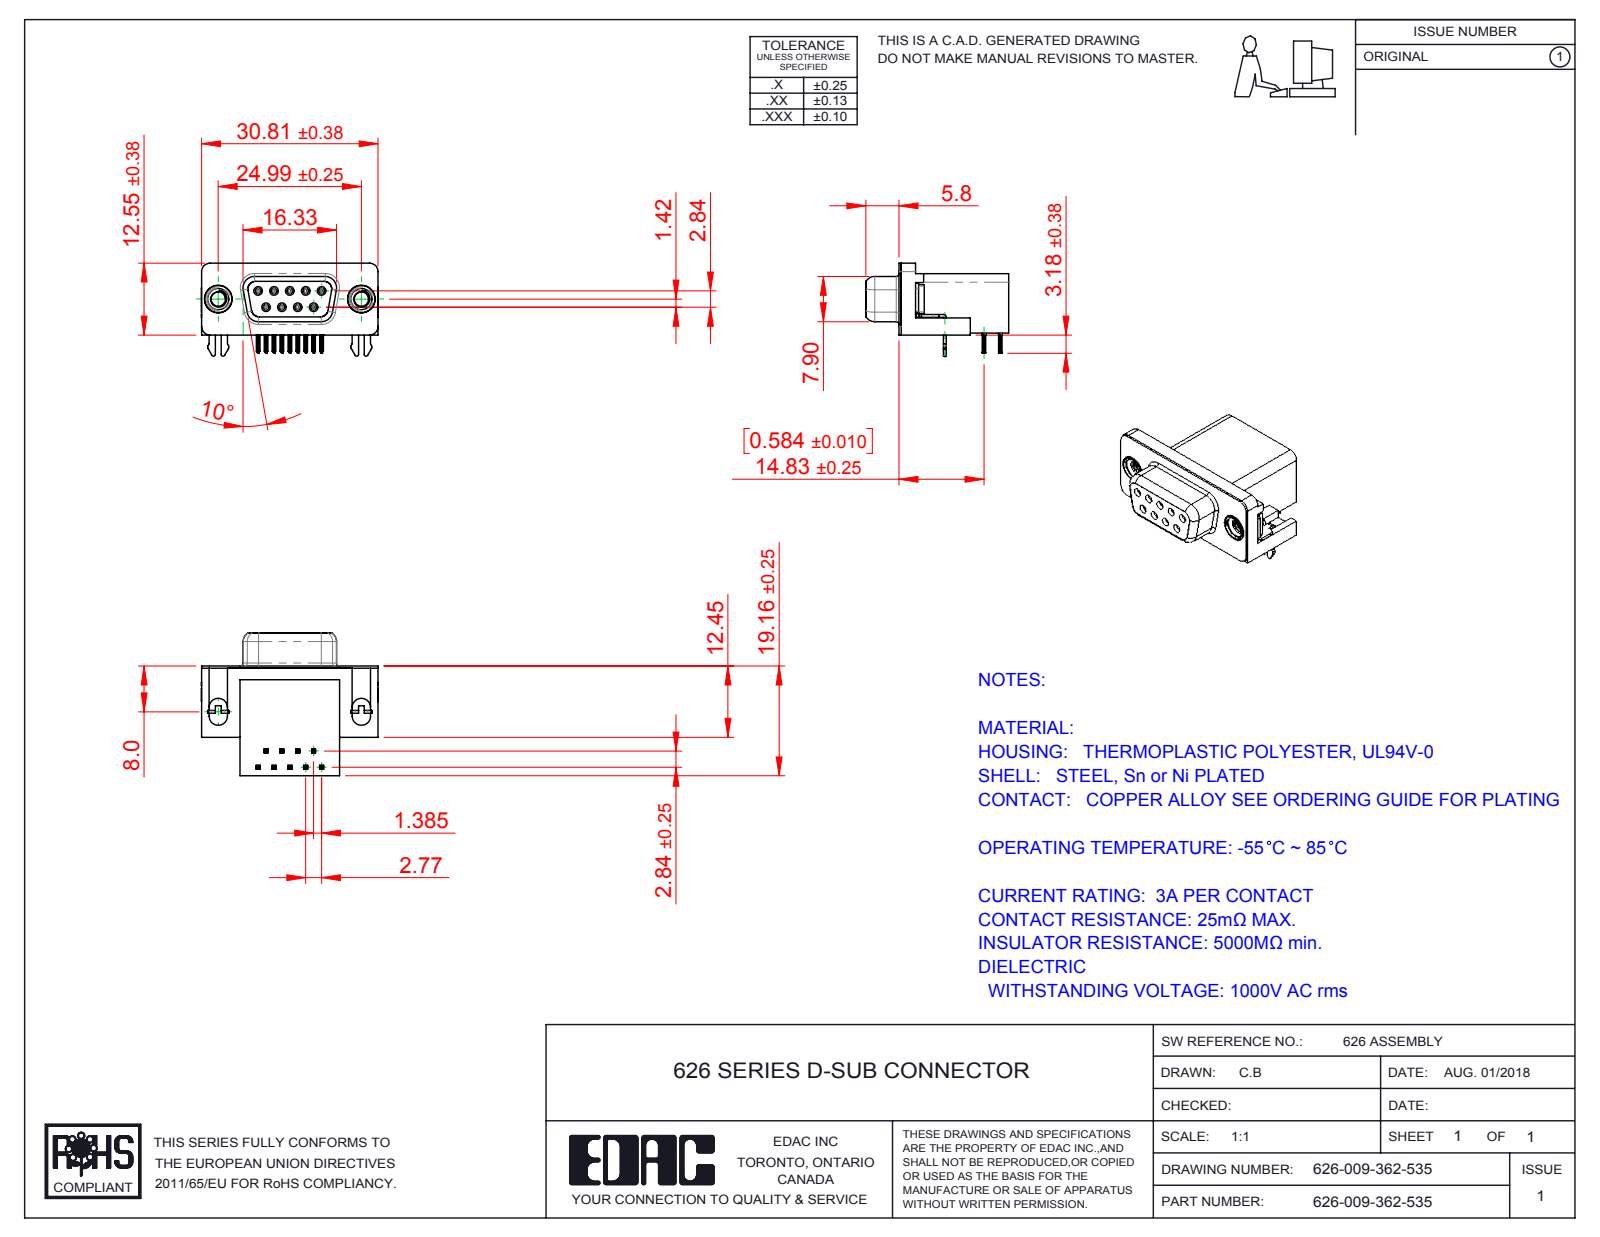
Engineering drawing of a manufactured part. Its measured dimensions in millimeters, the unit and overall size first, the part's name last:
Units: millimetres
Overall size (bounding box): 30.89 × 24.96 × 16.25
Round holes (diameter × count): ⌀0.8 ×9, ⌀0.9 ×9, ⌀2.5 ×2, ⌀4 ×2, ⌀4.8 ×2, ⌀5 ×2
Round bosses / shafts (diameter × count): ⌀1.2 ×9, ⌀4.9 ×2, ⌀4.75 ×2, ⌀3.9 ×2
Partial cylindrical surfaces — rounded edges, fillets, slot ends (radius × count): R0.1 ×72, R0.15 ×36, R0.35 ×18, R1 ×18, R0.5 ×10, R0.34 ×9, R0.25 ×8, R1.35 ×8
Main face-to-face distances: 0.4, 10.34, 0.35, 18.76, 19.16, 2.9, 2.5, 6.2, 16.26, 0.5
Hole centre spacings: 3.16, 2.77, 5.54, 5.03, 5.04, 8.31, 7.48, 7.49
Volume: 4 962 mm³ · Surface area: 5 800 mm²
Bodies: 15 solids, 1612 faces (716 planar, 428 cylindrical, 468 other)
Part name (STEP PRODUCT): 626 Contact Bottom; 626 Contact Top; 626 2 Prong Board Lock; 626 M3 Threaded Rivet (+3 more)
STEP written by: SolidWorks 2016 (CONFIG_CONTROL_DESIGN)
